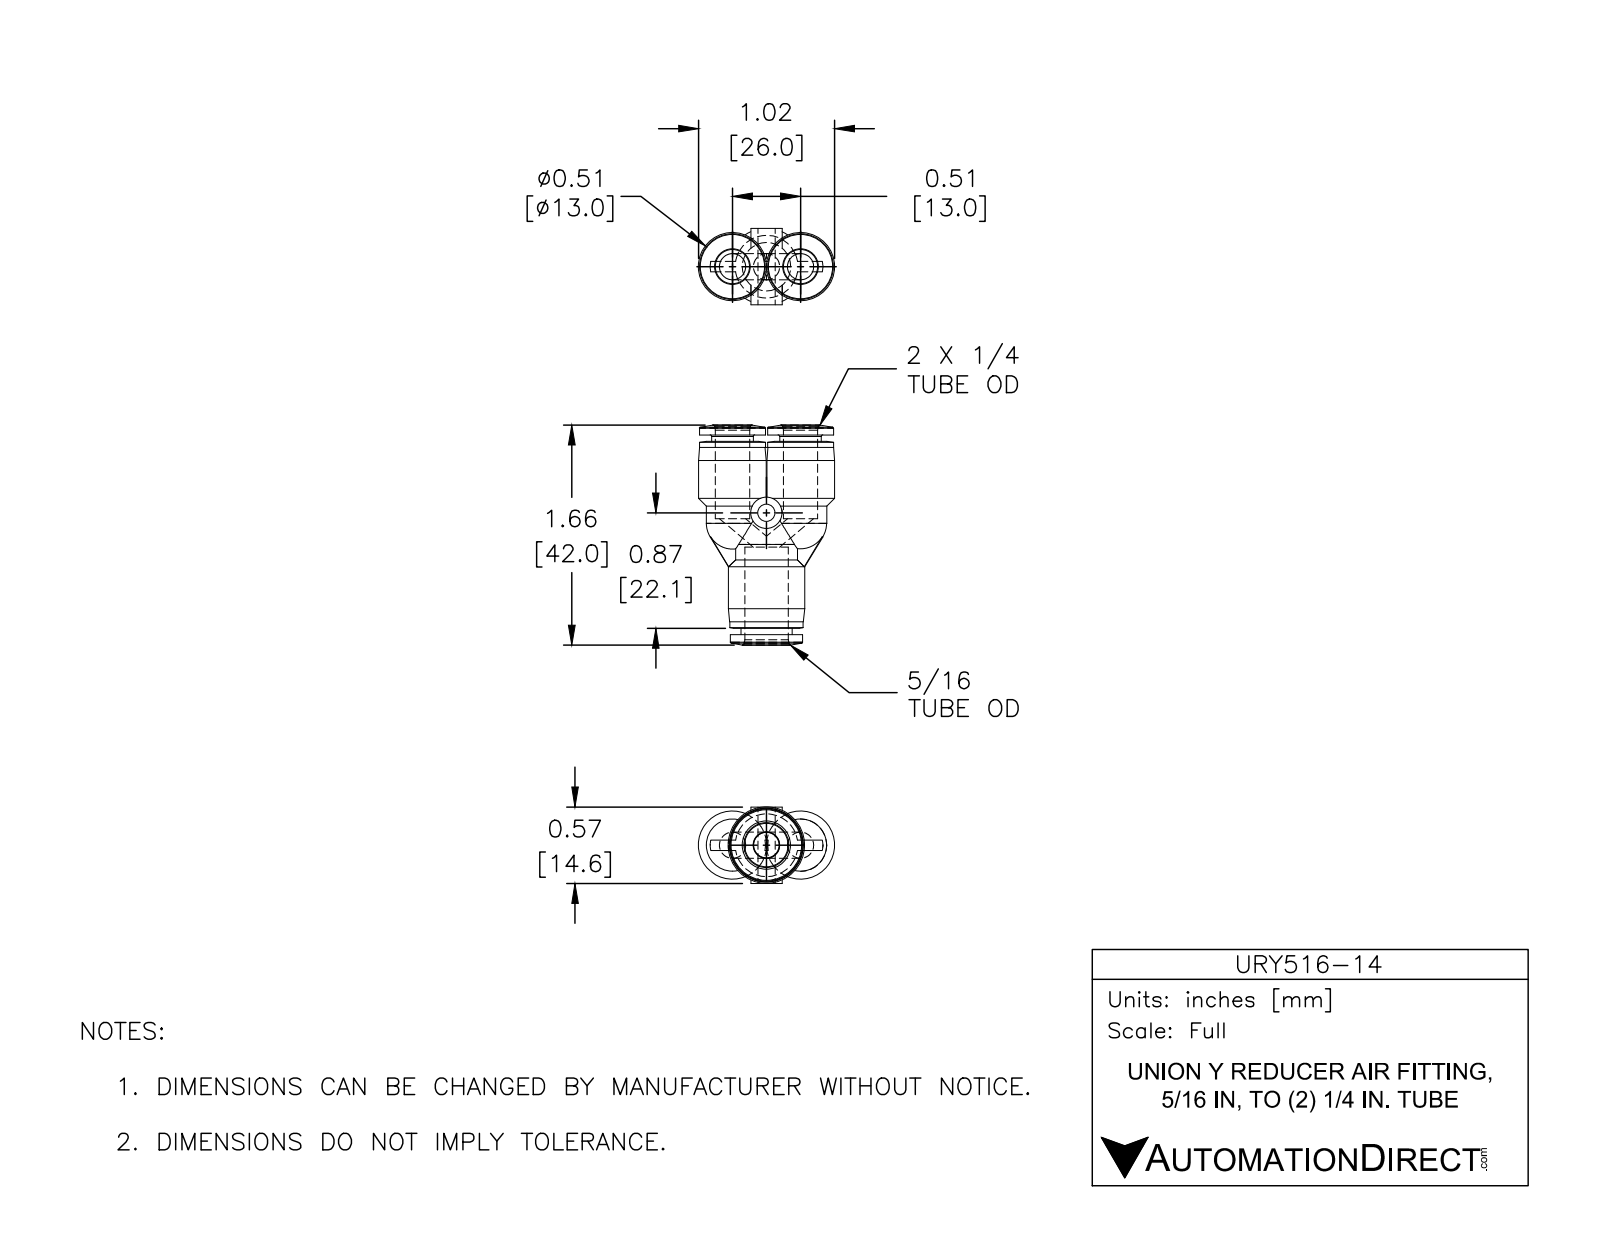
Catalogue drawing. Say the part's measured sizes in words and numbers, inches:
The part is named "URY516-14". Its 3-D file was written by "SolidWorks 2015 (CONFIG_CONTROL_DESIGN)". It is 1 solid with 113 faces: 19 planar, 40 cylindrical and 54 other. Overall it measures 1.656 by 1.024 by 0.575 inches. Its volume is 0.343 cubic inches and its surface area 7.627 square inches. Round holes: 2 of diameter 0.258, 1 of diameter 0.13, 1 of diameter 0.327. Round bosses or shafts: 2 of diameter 0.512, 2 of diameter 0.496, 2 of diameter 0.313, 1 of diameter 0.575, 1 of diameter 0.551, 1 of diameter 0.543, 1 of diameter 0.472, 1 of diameter 0.386. Partial cylindrical surfaces (rounded edges, fillets, slot ends): 2 of radius 0.197. The main face-to-face distances are 0.047, 1.455, 1.502, 1.407, 0.248, 0.327, 0.657, 0.61, 0.797, 0.844. The hole center spacings are 0.256, 0.512.
